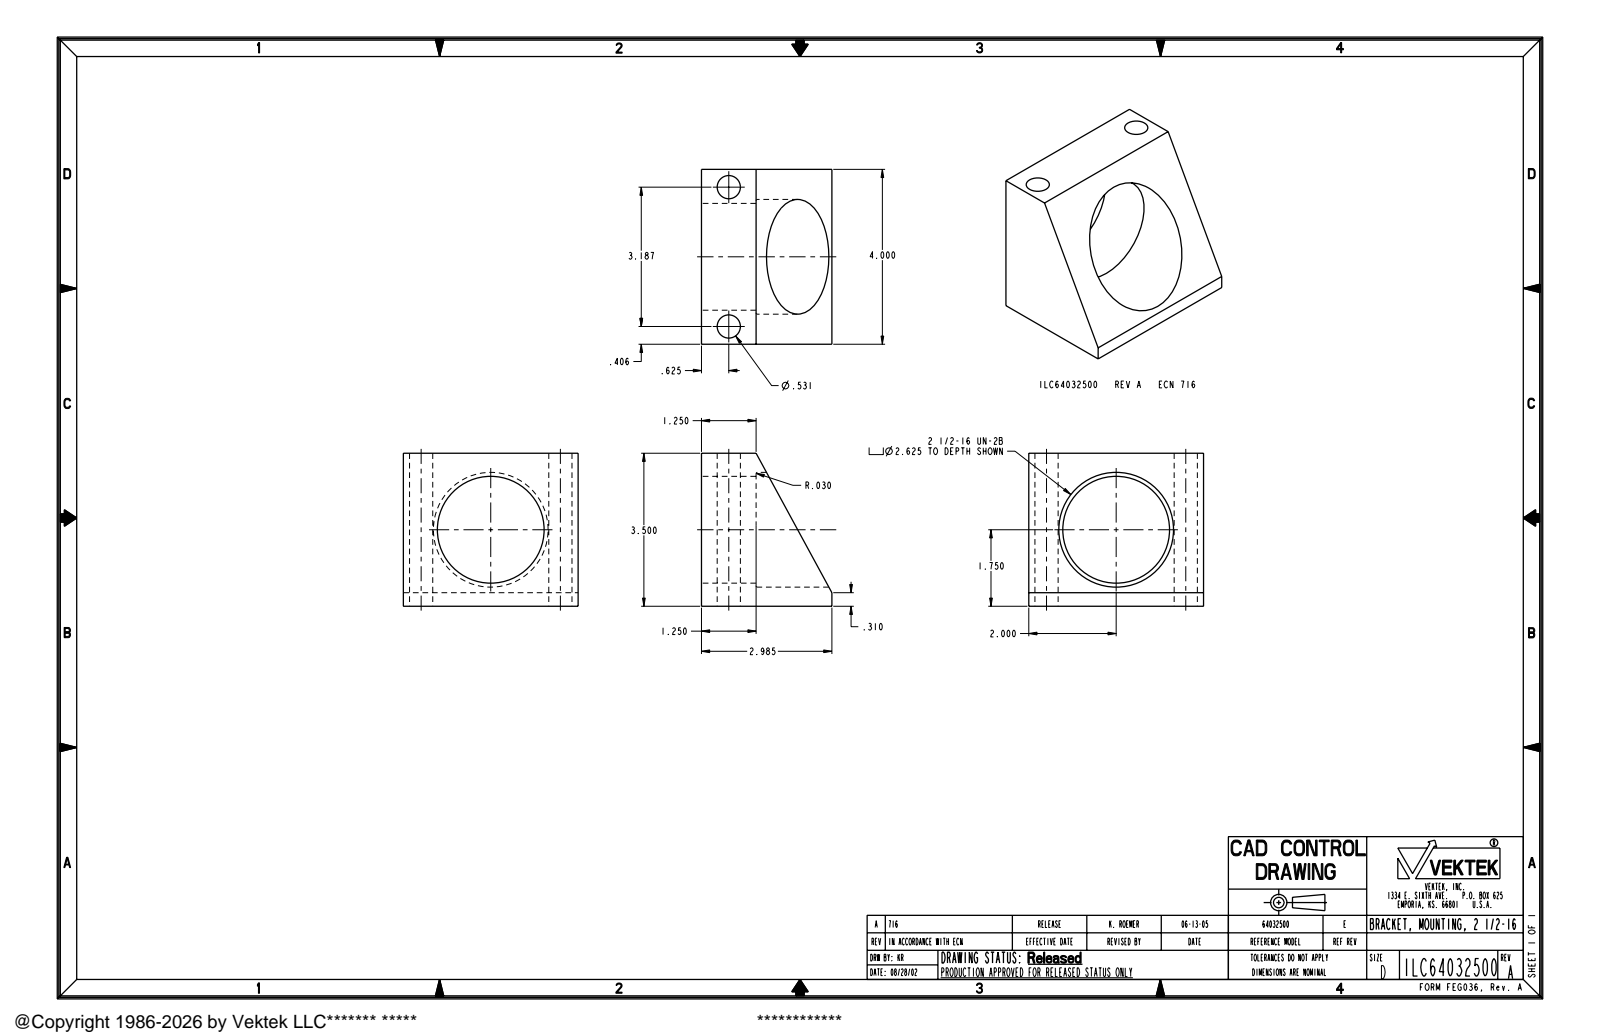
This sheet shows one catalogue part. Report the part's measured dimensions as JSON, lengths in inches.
{"part_name": "ILC64032500", "step_written_by": "PRO/ENGINEER BY PARAMETRIC TECHNOLOGY CORPORATION, 2004290 (AUTOMOTIVE_DESIGN_CC2)", "units": "inches", "bodies": {"solids": 1, "faces": 18, "planar": 8, "cylindrical": 8, "other": 2}, "overall_size": [4, 3.5, 2.985], "volume_in3": 18.16, "surface_area_in2": 80.07, "round_holes": [[0.531, 2], [2.443, 1], [2.625, 1]], "face_to_face_distances": [4, 3.5, 2.985, 1.735, 1.25], "hole_center_spacings": [3.187]}
